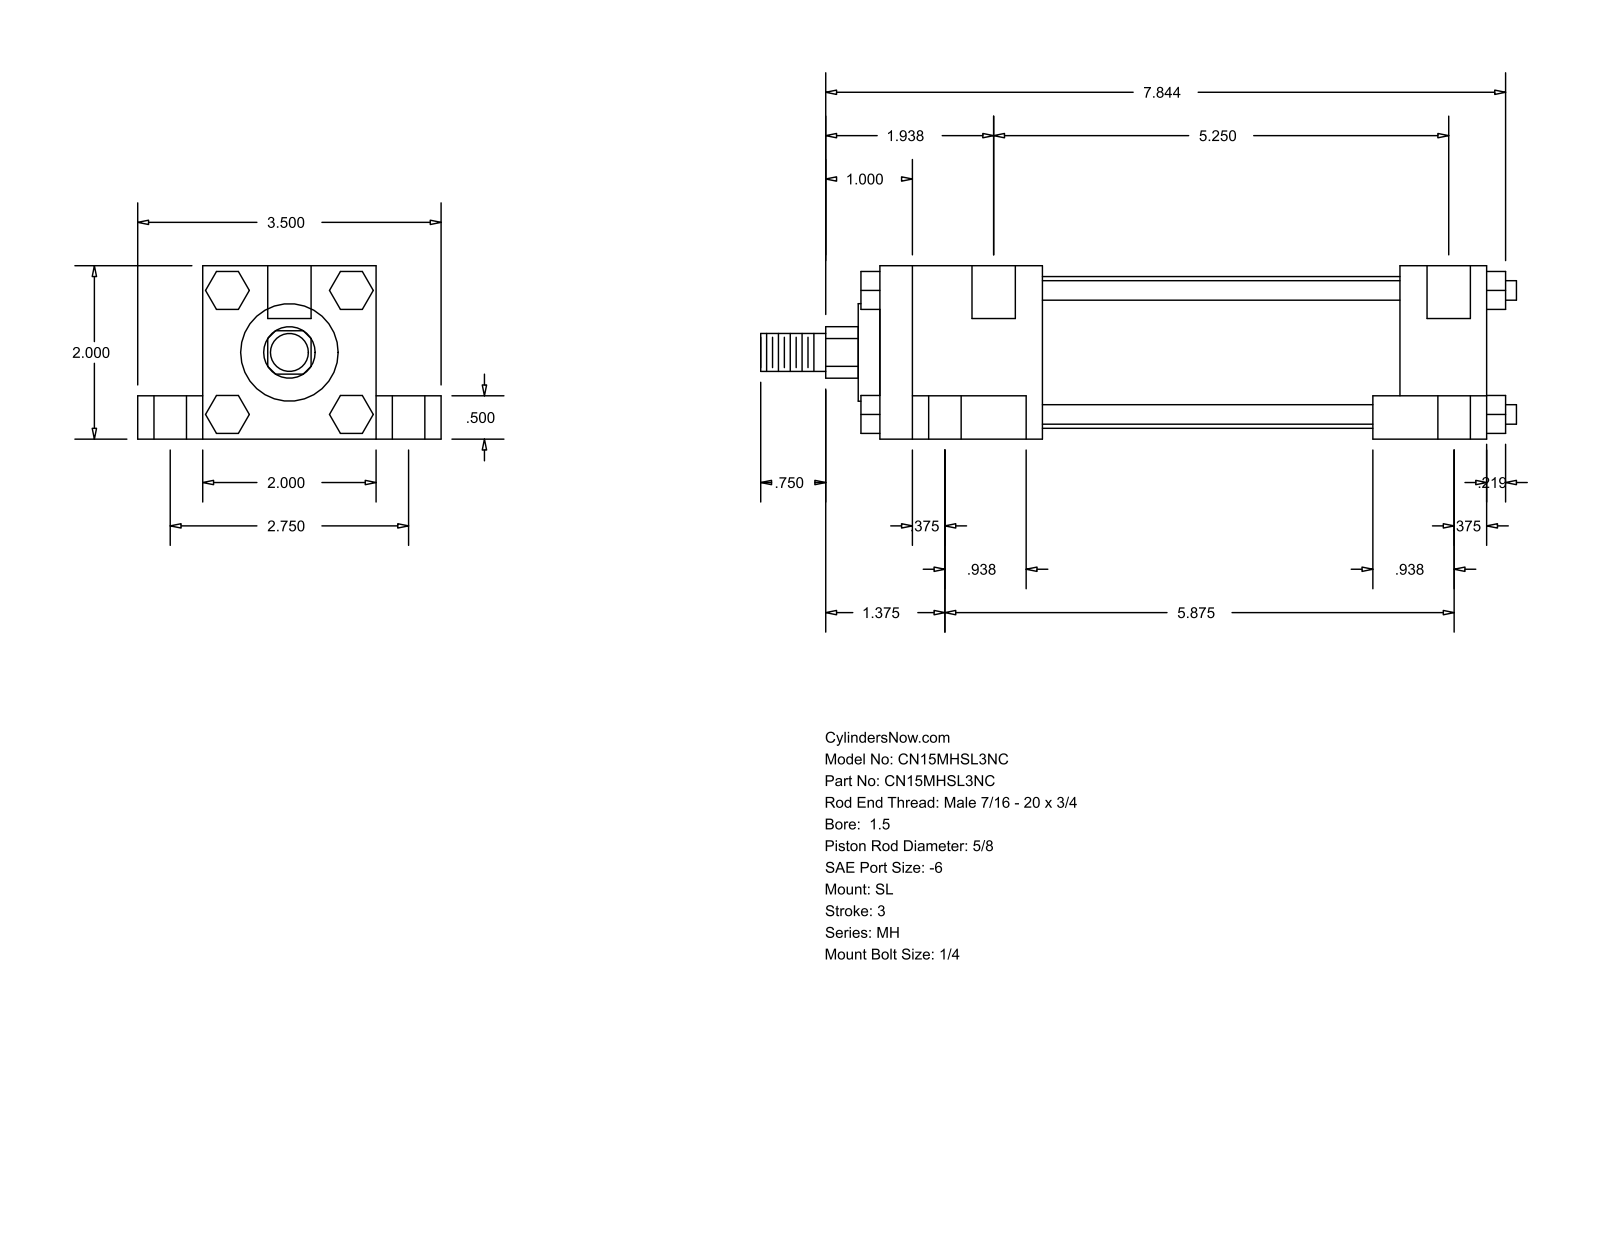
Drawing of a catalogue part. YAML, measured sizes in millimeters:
part_name: "MH_SL__0150_0.625"
step_written_by: "GSSL Pune (CONFIG_CONTROL_DESIGN)"
units: millimeters
bodies: {solids: 0, faces: 148, planar: 112, cylindrical: 36, other: 0}
overall_size: [221.46, 88.9, 50.8]
round_holes:
  - {diameter: 5.56, count: 4}
  - {diameter: 9.53, count: 4}
  - {diameter: 15.88, count: 4}
  - {diameter: 12.7, count: 2}
round_bosses_or_shafts:
  - {diameter: 5.71, count: 4}
  - {diameter: 44.45, count: 1}
  - {diameter: 28.57, count: 1}
  - {diameter: 15.88, count: 1}
  - {diameter: 11.11, count: 1}
partial_cylinders:
  - {radius: 7.54, count: 1}
face_to_face_distances: [50.8, 38.1, 19.05, 12.7, 69.85, 177.8, 25.4, 9.52, 33.34, 134.94]
hole_center_spacings: [34.96, 36.65, 37.73, 69.84, 136.52, 139.39, 142.46, 149.23]
